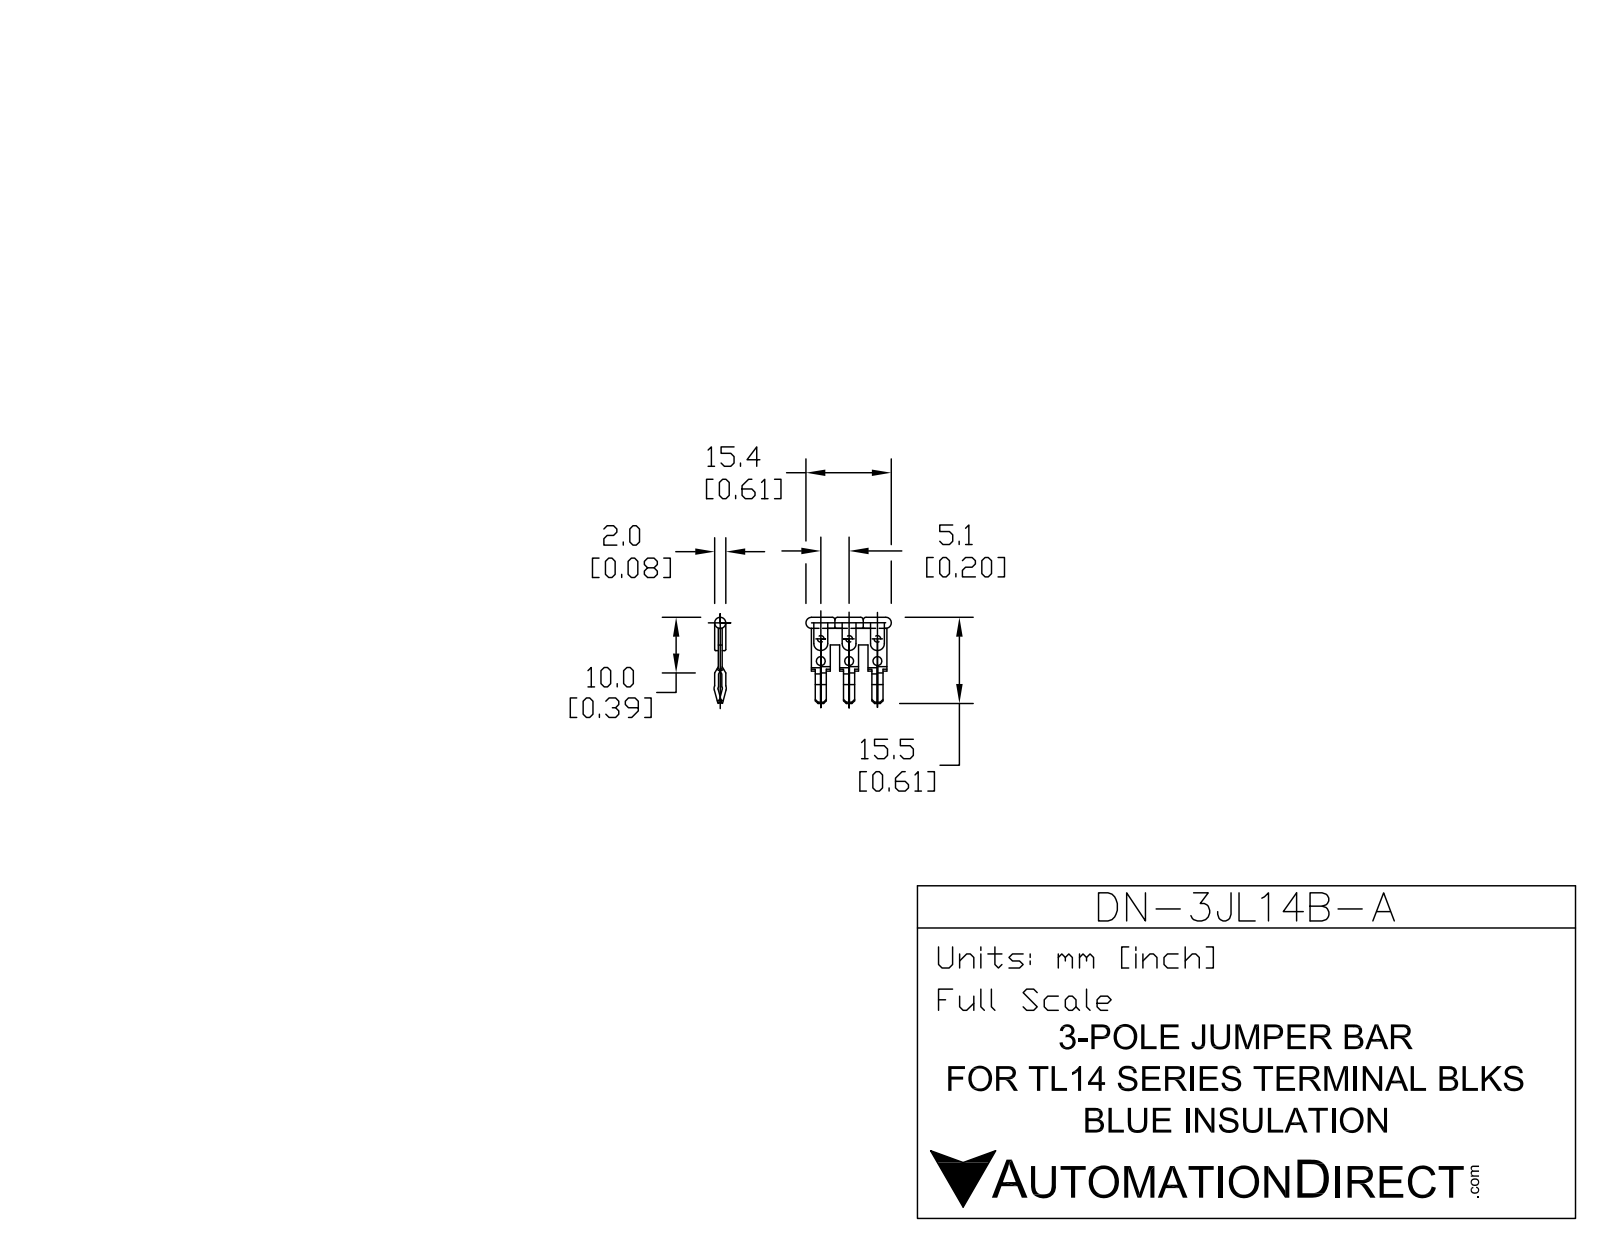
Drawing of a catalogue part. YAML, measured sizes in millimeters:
part_name: "43531_03_BLS_DN-3JL14B-A"
step_written_by: "SolidWorks 2013 (AUTOMOTIVE_DESIGN)"
units: millimeters
bodies: {solids: 2, faces: 217, planar: 113, cylindrical: 80, other: 24}
overall_size: [15.5, 15.2, 2.08]
volume: 186
surface_area: 550
round_holes:
  - {diameter: 1.2, count: 3}
  - {diameter: 1.3, count: 3}
round_bosses_or_shafts:
  - {diameter: 2, count: 1}
partial_cylinders:
  - {radius: 0.25, count: 12}
  - {radius: 0.48, count: 4}
  - {radius: 0.7, count: 4}
  - {radius: 0.5, count: 3}
  - {radius: 1.25, count: 3}
face_to_face_distances: [0.7, 0.65, 1.35, 5.1, 1.2, 2, 0.55, 10.2, 1.3, 2.25]
hole_center_spacings: [5.1, 6.48, 4, 10.2, 10.96]
